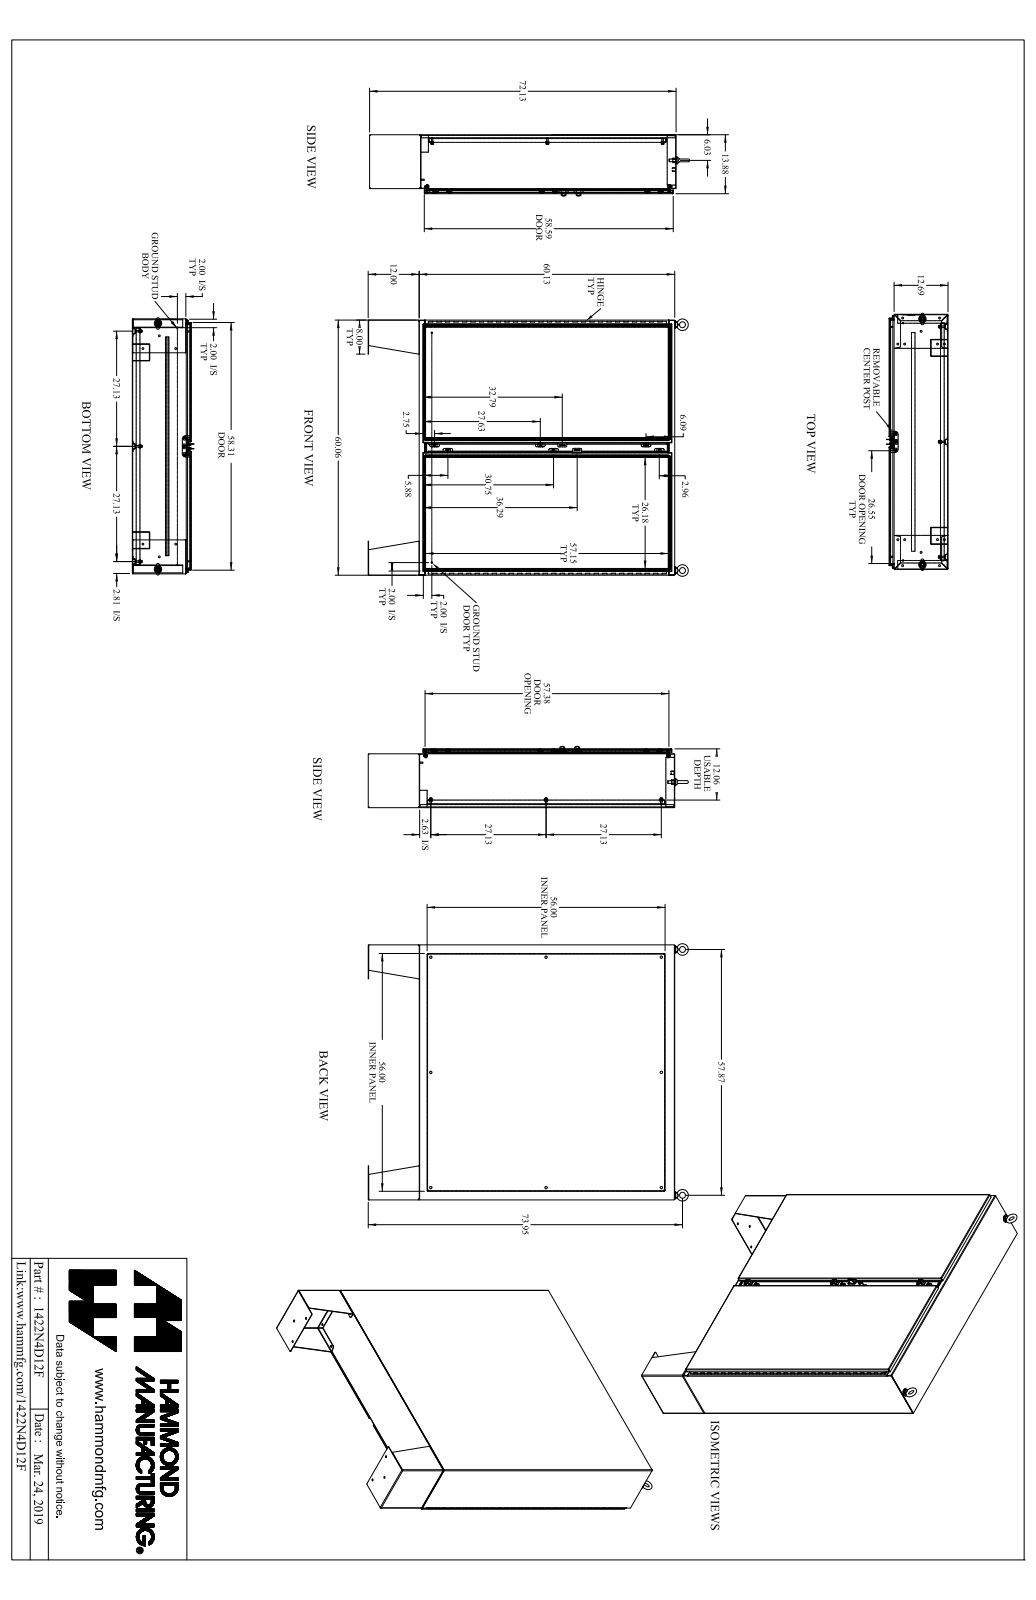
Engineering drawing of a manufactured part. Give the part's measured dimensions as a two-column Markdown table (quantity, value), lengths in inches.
| quantity | value |
| --- | --- |
| part name | 1422N4D12F_Default |
| STEP written by | SolidWorks 2019 (CONFIG_CONTROL_DESIGN) |
| units | inches |
| bodies | 107 solids, 3407 faces (1754 planar, 1441 cylindrical, 212 other) |
| overall size | 75.778 × 61.121 × 14.468 |
| volume | 1 692 in³ |
| surface area | 34 070 in² |
| round holes (diameter × count) | 0.304 × 20, 0.437 × 14, 0.307 × 8, 0.563 × 8, 0.213 × 6, 0.265 × 6, 0.375 × 6, 0.445 × 6, 0.201 × 3, 0.25 × 3, 0.313 × 3, 0.11 × 2 |
| round bosses / shafts (diameter × count) | 1 × 8, 0.65 × 8, 0.375 × 8, 0.33 × 8, 0.5 × 6, 0.39 × 6, 0.244 × 6, 0.281 × 4 |
| partial cylindrical surfaces (radius × count) | 0.048 × 67, 0.143 × 67, 0.25 × 34, 0.06 × 18, 0.116 × 12, 0.141 × 12, 0.185 × 12, 0.187 × 9 |
| main face-to-face distances | 0.095, 13.78, 13.685, 13.875, 11.998, 0.125, 12.093, 1.687, 1.782, 12.218 |
| hole center spacings | 6, 58.513, 12, 59.429, 18, 60.924, 24, 62.959 |
